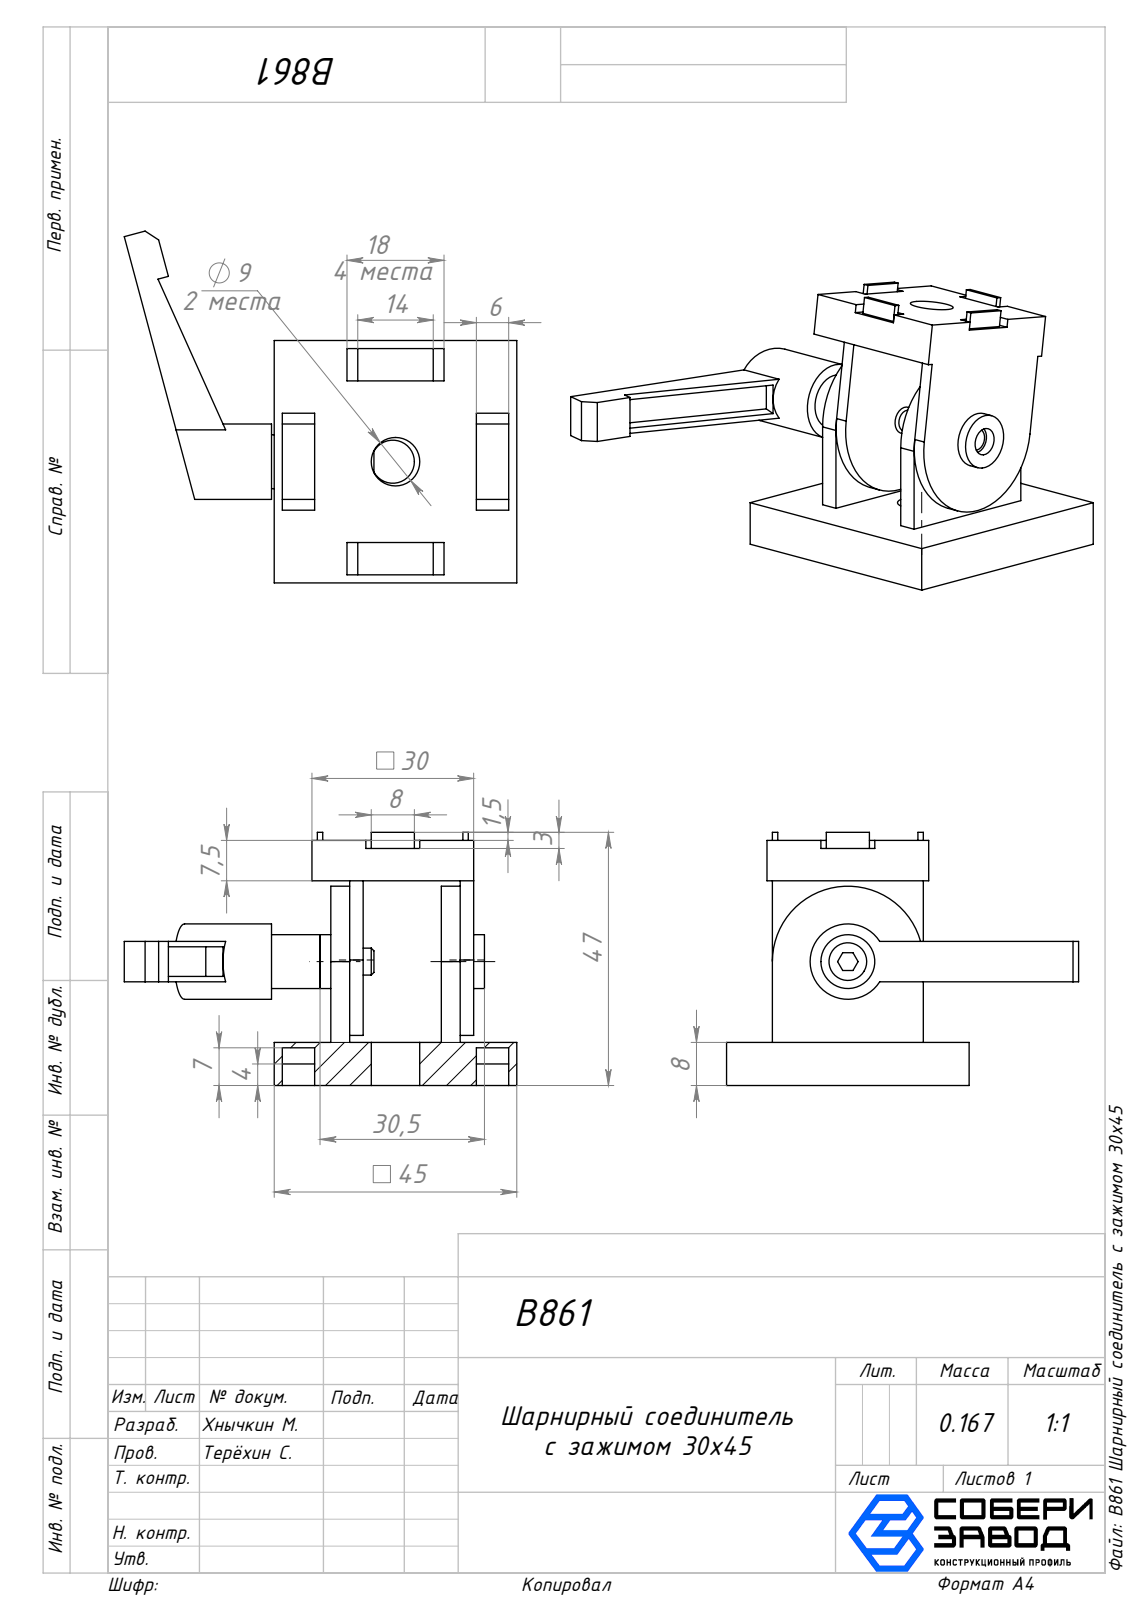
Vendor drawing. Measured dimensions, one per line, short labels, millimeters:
name: Винт_00; Соединитель_00; Винт с рукояткой_00; B861 Шарнирный соединитель c зажимом 30х45 (+4 more)
written by: SolidWorks 2025 (AUTOMOTIVE_DESIGN)
unit: mm
bodies: 7 solids, 177 faces (133 planar, 42 cylindrical, 2 other)
size: 72.82 × 65.31 × 48.72
volume: 32 314 mm³; area: 20 680 mm²
holes: 1× ⌀3, 1× ⌀4, 1× ⌀5, 1× ⌀6, 1× ⌀8, 1× ⌀9
bosses: 1× ⌀14, 1× ⌀10, 1× ⌀7
rounds: 2× R14
face distances: 20.5, 6, 8, 3.5, 2.5, 7.5, 24, 1, 7, 23
